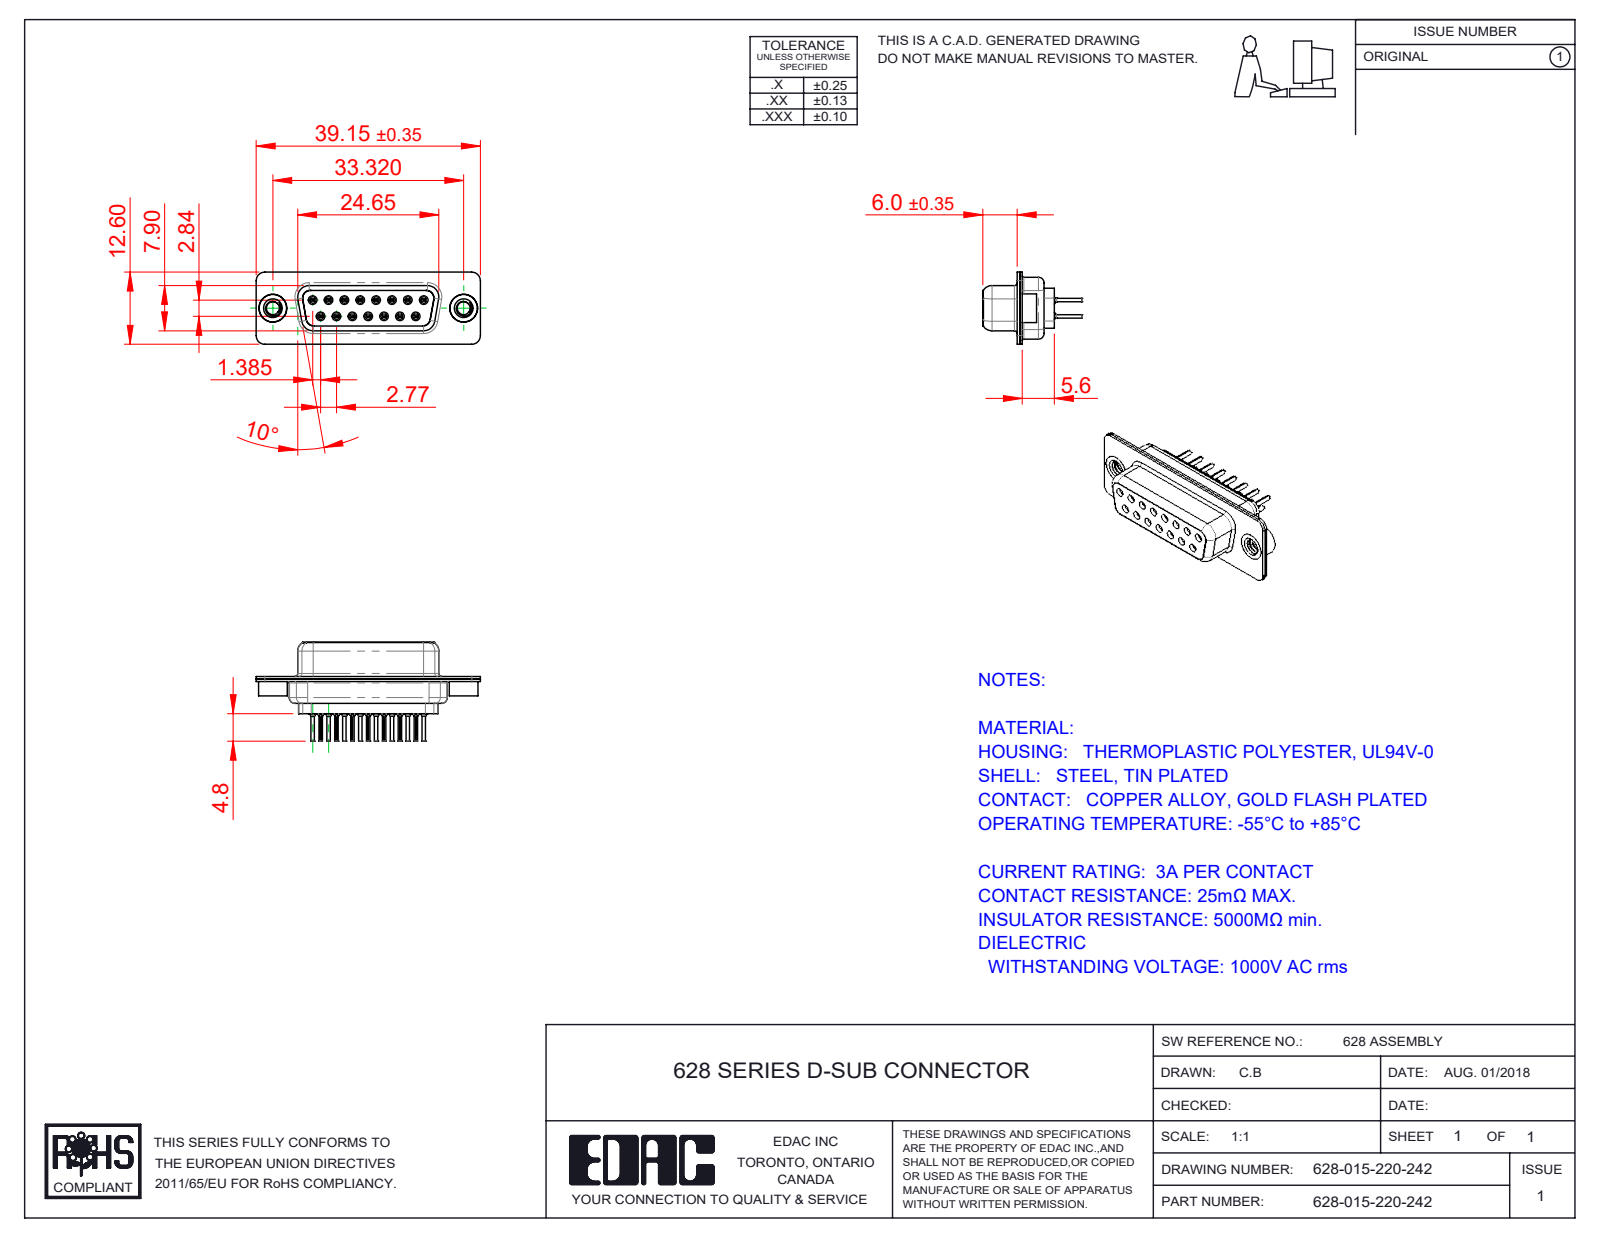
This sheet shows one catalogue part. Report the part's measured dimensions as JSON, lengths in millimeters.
{"part_name": "628 Shell Front_15 Contacts; 628-015-220-242; 628 Shell Rear_15 Contacts; 628 4-40 Threaded Rivet (+3 more)", "step_written_by": "SolidWorks 2020 (CONFIG_CONTROL_DESIGN)", "units": "millimeters", "bodies": {"solids": 20, "faces": 2180, "planar": 532, "cylindrical": 630, "other": 1018}, "overall_size": [39.15, 17.3, 12.6], "volume_mm3": 2538, "surface_area_mm2": 6315, "round_holes": [[0.2, 15], [0.8, 15], [0.9, 15], [1.1, 15], [1.6, 15], [1.7, 8], [2.26, 2], [4, 2], [4.05, 2], [4.85, 2]], "round_bosses_or_shafts": [[2, 15], [1.5, 15], [1.2, 15], [0.6, 15], [5, 2], [4.95, 2], [4.8, 2]], "partial_cylinders_radius": [[0.1, 30], [1.5, 18], [0.28, 15], [2, 12], [1.35, 8], [0.25, 4], [0.5, 4], [0.6, 4]], "face_to_face_distances": [0.45, 0.4, 0.9, 6.6, 1.9, 8.5, 1.4, 0.85, 7.05, 7.45], "hole_center_spacings": [3.16, 2.77, 5.54, 8.31, 11.08, 5.03, 5.04, 7.48]}
